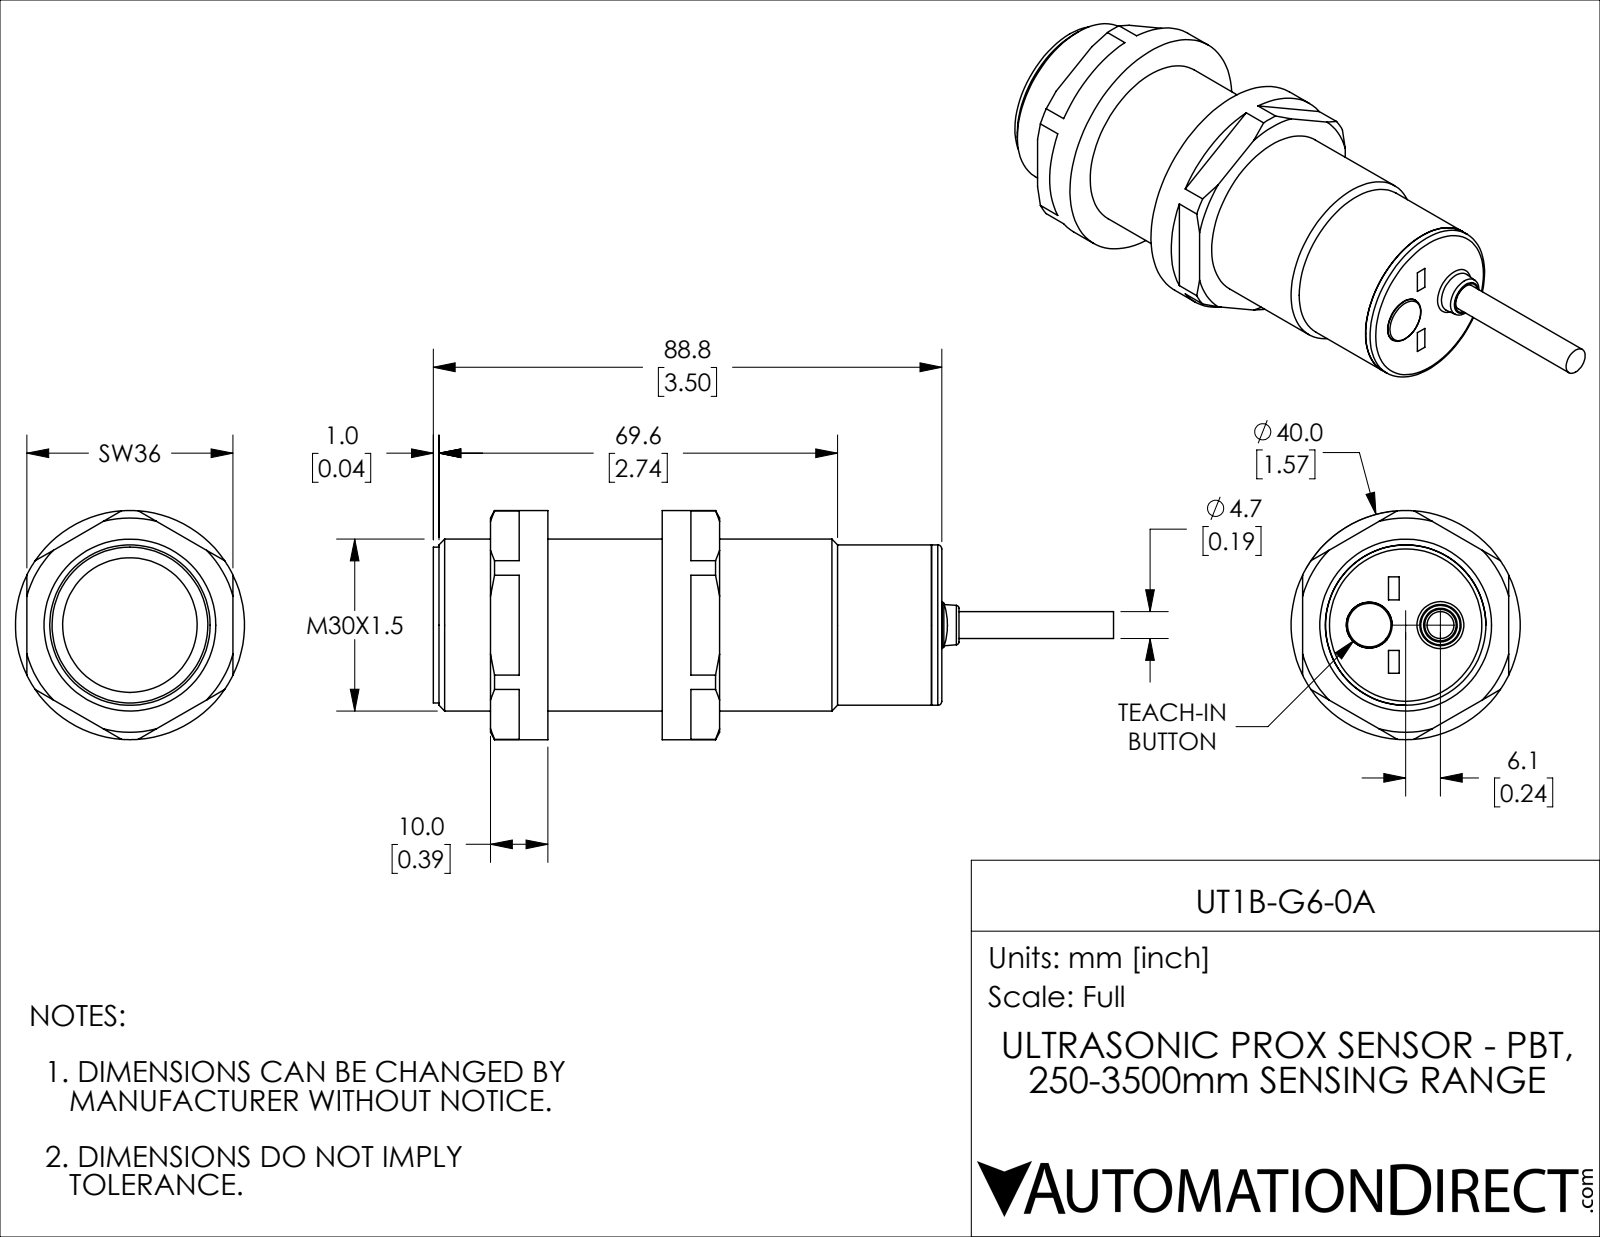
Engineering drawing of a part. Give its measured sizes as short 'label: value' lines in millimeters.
name: UT1B-G6-0A
written by: SolidWorks 2018 (AUTOMOTIVE_DESIGN)
unit: mm
bodies: 7 solids, 101 faces (43 planar, 26 cylindrical, 32 other)
size: 118.8 × 40 × 40
volume: 71 057 mm³; area: 19 190 mm²
holes: 1× ⌀4.7, 1× ⌀8, 1× ⌀23.5, 1× ⌀30
bosses: 1× ⌀40, 1× ⌀28, 1× ⌀27.2
face distances: 86, 30, 10, 20, 5, 87.8, 39, 47, 19, 67
hole spacings: 6.07, 6.36, 12.43
